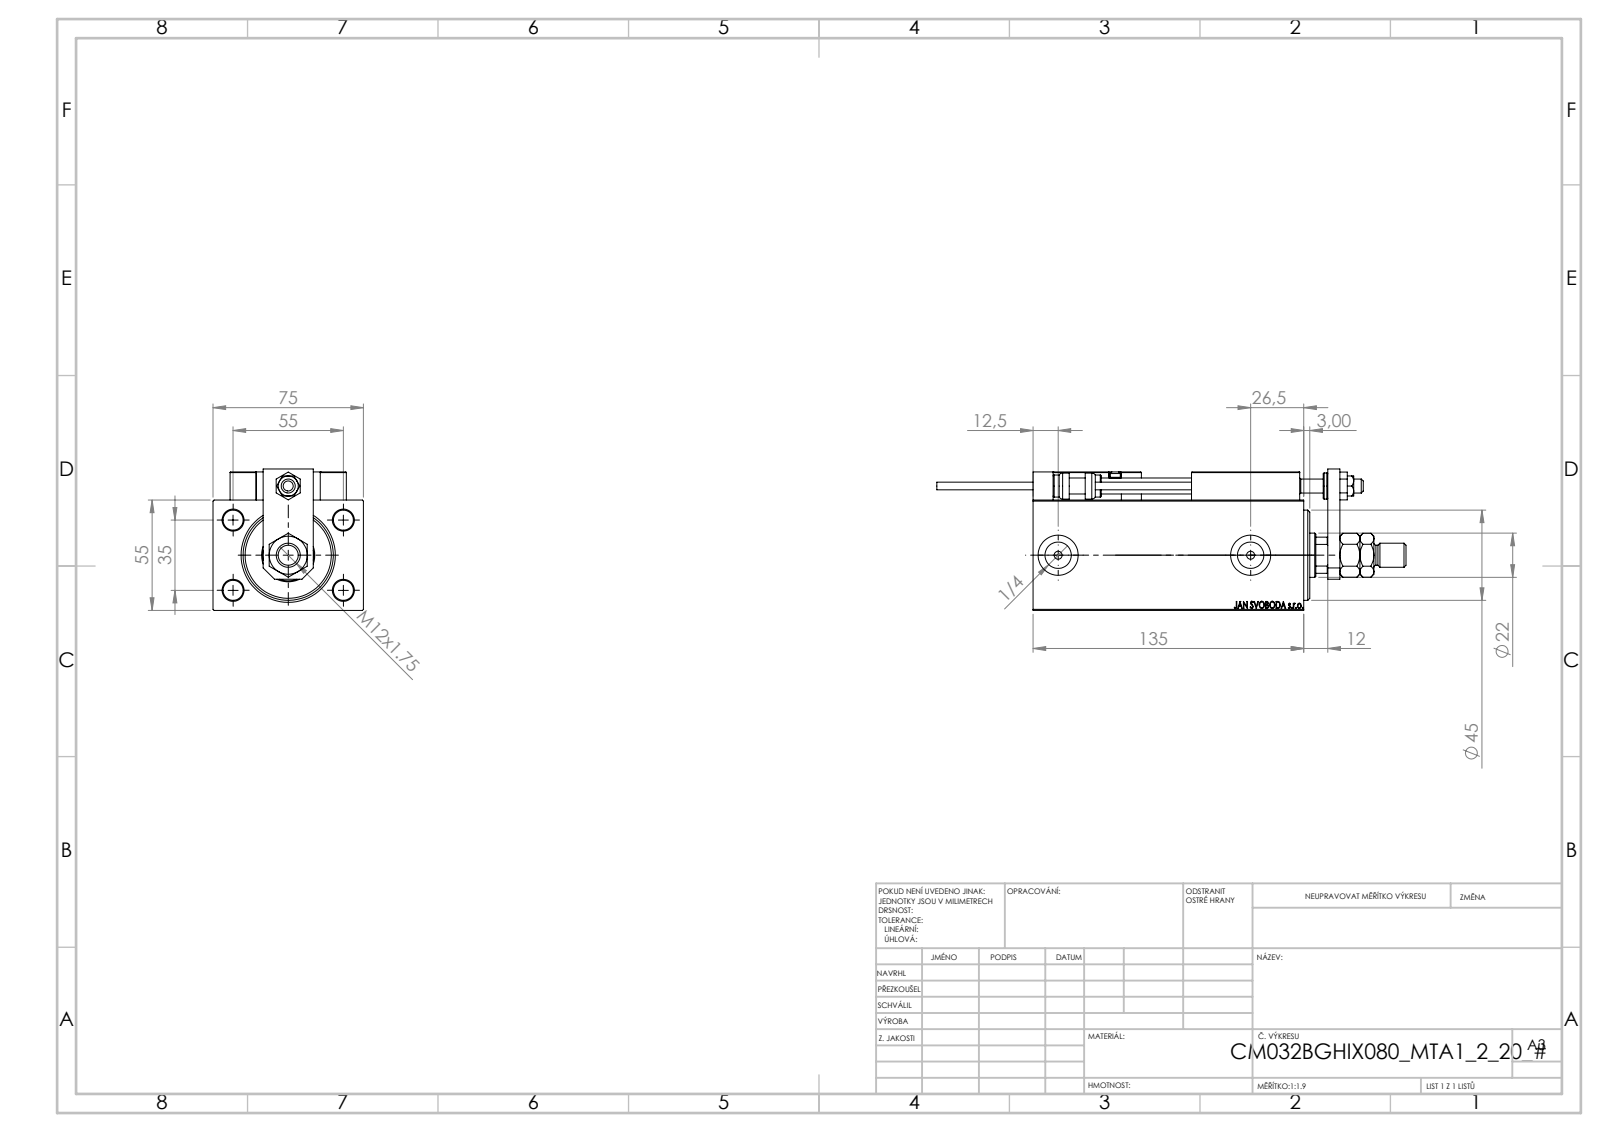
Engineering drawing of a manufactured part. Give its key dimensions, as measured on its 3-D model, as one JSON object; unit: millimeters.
{"part_name": "V450CM_VC_B; KONCOVKA; NUT_D12; X_Y_MTA (+7 more)", "step_written_by": "SolidWorks 2019 (CONFIG_CONTROL_DESIGN)", "units": "millimeters", "bodies": {"solids": 25, "faces": 1367, "planar": 576, "cylindrical": 188, "other": 603}, "overall_size": [234, 75, 70.5], "volume_mm3": 569299, "surface_area_mm2": 108503, "round_holes": [[4, 6], [8, 5], [3.2, 4], [10, 4], [5, 2], [13.16, 2], [20, 2], [7, 1], [10.5, 1], [16.5, 1], [22, 1], [25.5, 1]], "round_bosses_or_shafts": [[5, 2], [3.8, 2], [13, 1], [12, 1], [11, 1], [10, 1]], "partial_cylinders_radius": [[0.3, 30], [3, 2], [10.5, 1]], "face_to_face_distances": [55, 75, 10, 12, 14, 69, 7, 18, 25, 3], "hole_center_spacings": [32.6, 11.37, 20, 29.59, 29.69, 32.33, 35, 36.06]}
